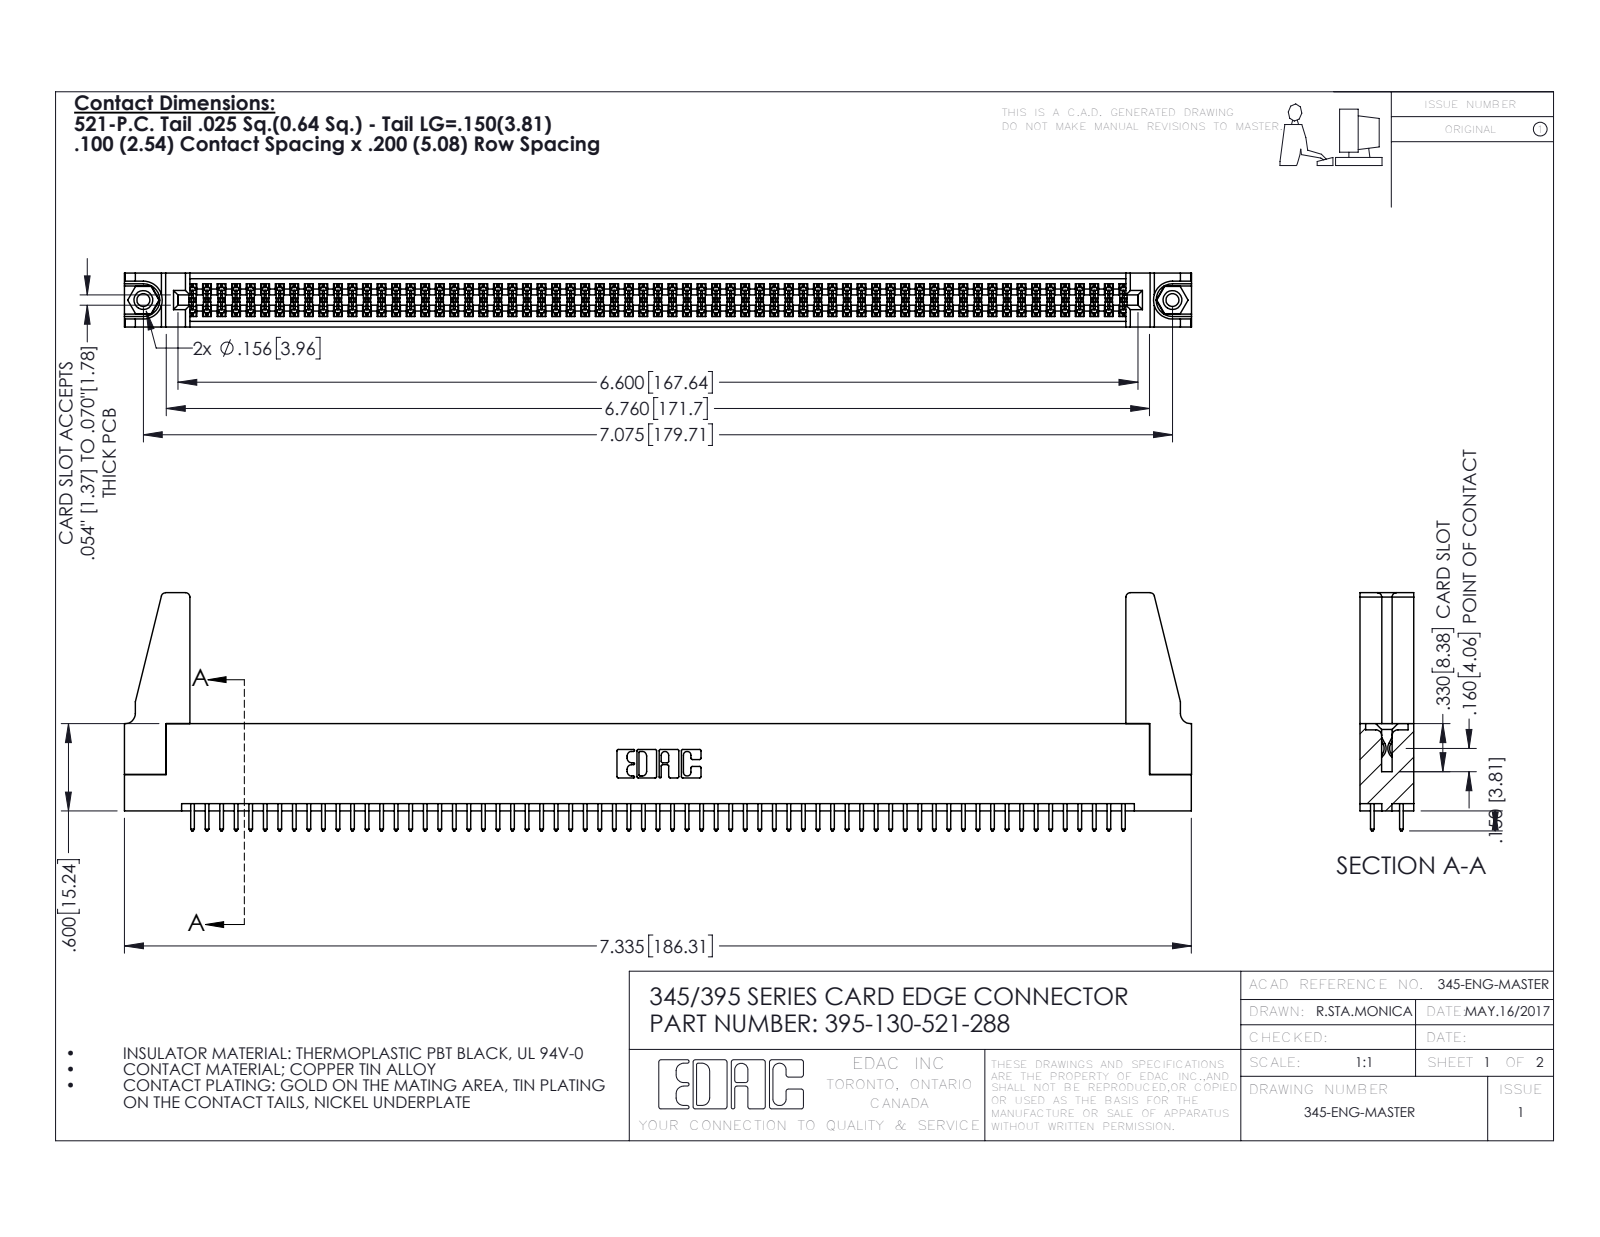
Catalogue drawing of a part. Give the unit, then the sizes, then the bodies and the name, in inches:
Units: inches
Overall size (bounding box): 7.336 × 1.637 × 0.37
Round holes (diameter × count): ⌀0.089 ×2, ⌀0.125 ×2, ⌀0.156 ×2, ⌀0.064 ×1
Round bosses / shafts (diameter × count): ⌀0.155 ×2
Partial cylindrical surfaces — rounded edges, fillets, slot ends (radius × count): R0.006 ×195, R0.01 ×130, R0.01 ×22, R0.03 ×8, R0.007 ×6, R0.031 ×6, R0.026 ×3, R0.014 ×2
Main face-to-face distances: 0.072, 0.298, 0.37, 0.2, 0.098, 0.272, 0.025, 0.225, 0.175, 0.149
Hole centre spacings: 0.27, 6.839, 7.075
Volume: 1.313 in³ · Surface area: 46.83 in²
Bodies: 135 solids, 6750 faces (4442 planar, 2292 cylindrical, 16 other)
Part name (STEP PRODUCT): 345 Part_Flush Mounting Lugs - 0.156 Dia-TH; 345-220-078_345-220-088; 345-292-001_345-293-121; 345-250-001_345-250-001-102 (+1 more)
STEP written by: SolidWorks 2016 (CONFIG_CONTROL_DESIGN)
